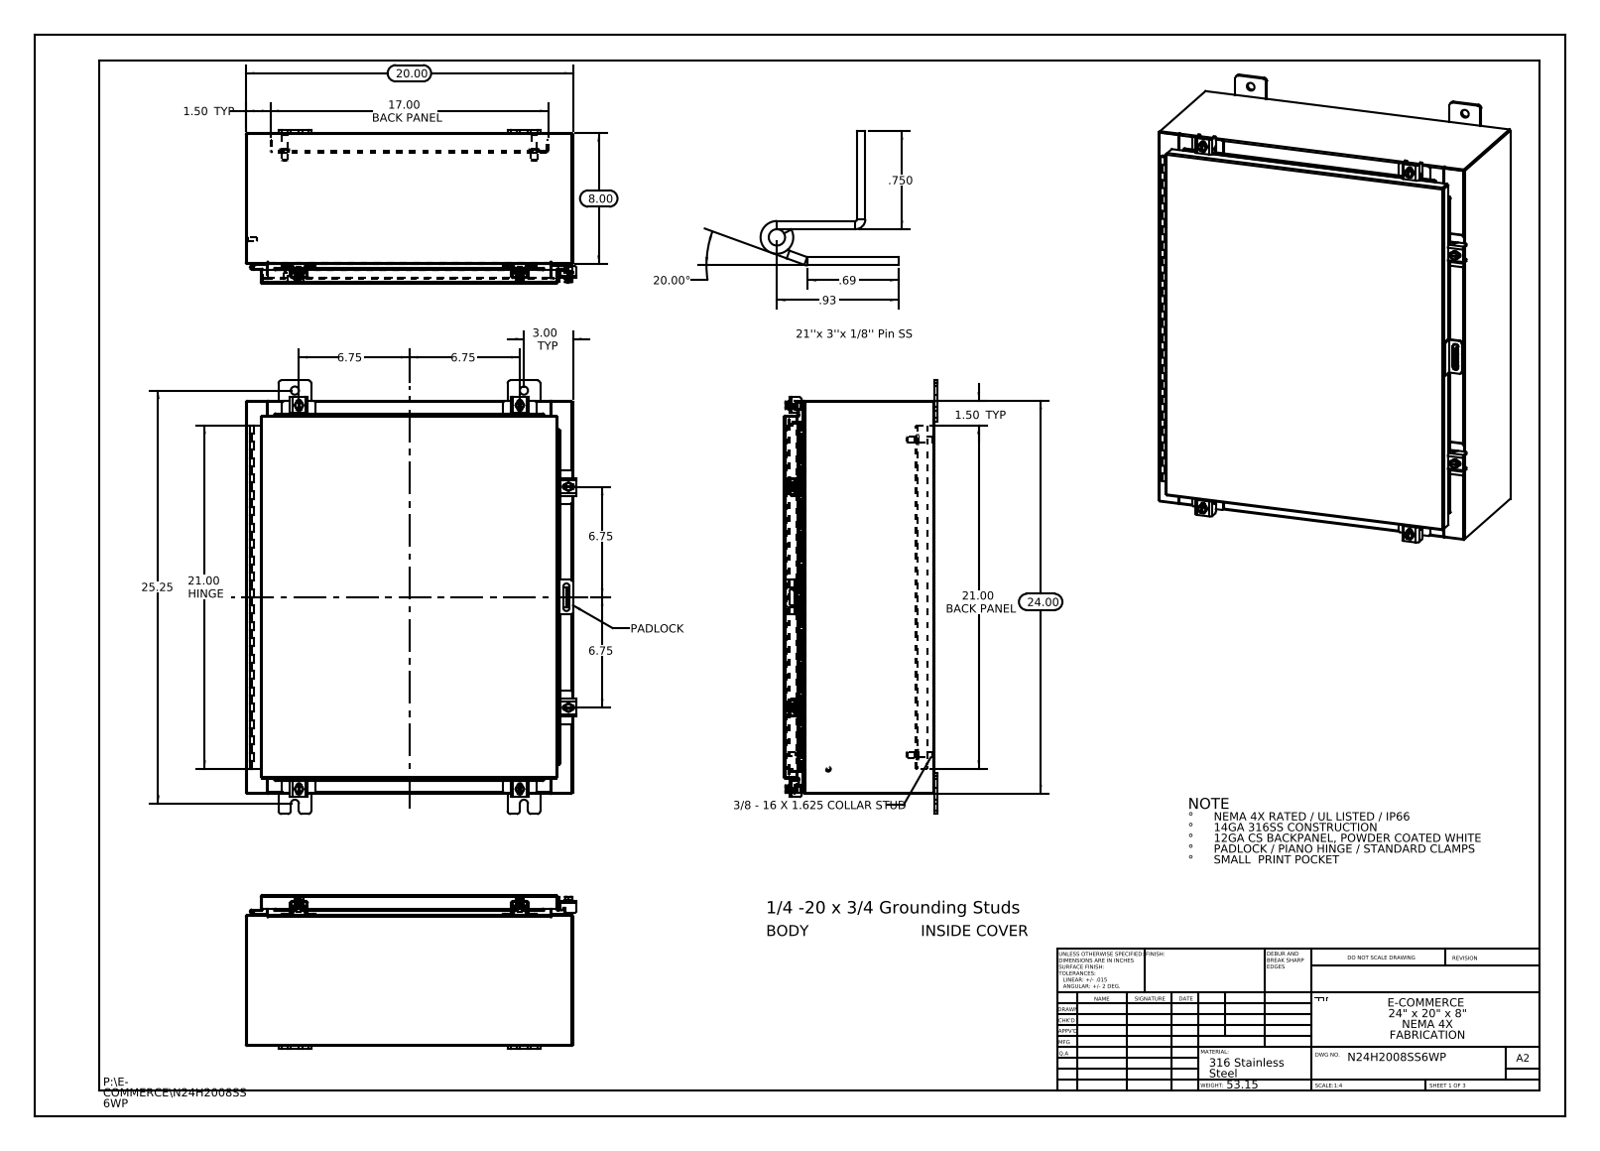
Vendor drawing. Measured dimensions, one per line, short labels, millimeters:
name: N24H2008SS6WP Cover; N24H2008SS6WP Mounting Studs; Quarter-20 CD Stud; N24H2008SS6WP Backpanel (+8 more)
written by: SolidWorks 2013 (CONFIG_CONTROL_DESIGN)
unit: mm
bodies: 49 solids, 1735 faces (914 planar, 713 cylindrical, 108 other)
size: 673.1 × 513.4 × 238.5
volume: 3 064 000 mm³; area: 3 041 000 mm²
holes: 8× ⌀12.7, 6× ⌀5.4, 6× ⌀6.6, 2× ⌀3.2, 1× ⌀3.2
bosses: 7× ⌀6.4, 6× ⌀12.7, 6× ⌀10.1, 4× ⌀15.9, 4× ⌀9.5, 4× ⌀8.4, 2× ⌀8, 2× ⌀6
rounds: 30× R1.5, 25× R0.3, 24× R4.8, 21× R2.2, 12× R3, 12× R3.6, 10× R3.2, 9× R1.3
face distances: 1.9, 231.8, 229.9, 233.7, 2.6, 506.1, 25.4, 27.3, 204.5, 206.4
hole spacings: 542.8, 653.8, 342.9, 10.9, 23.7, 47.2, 57.8, 57.8
